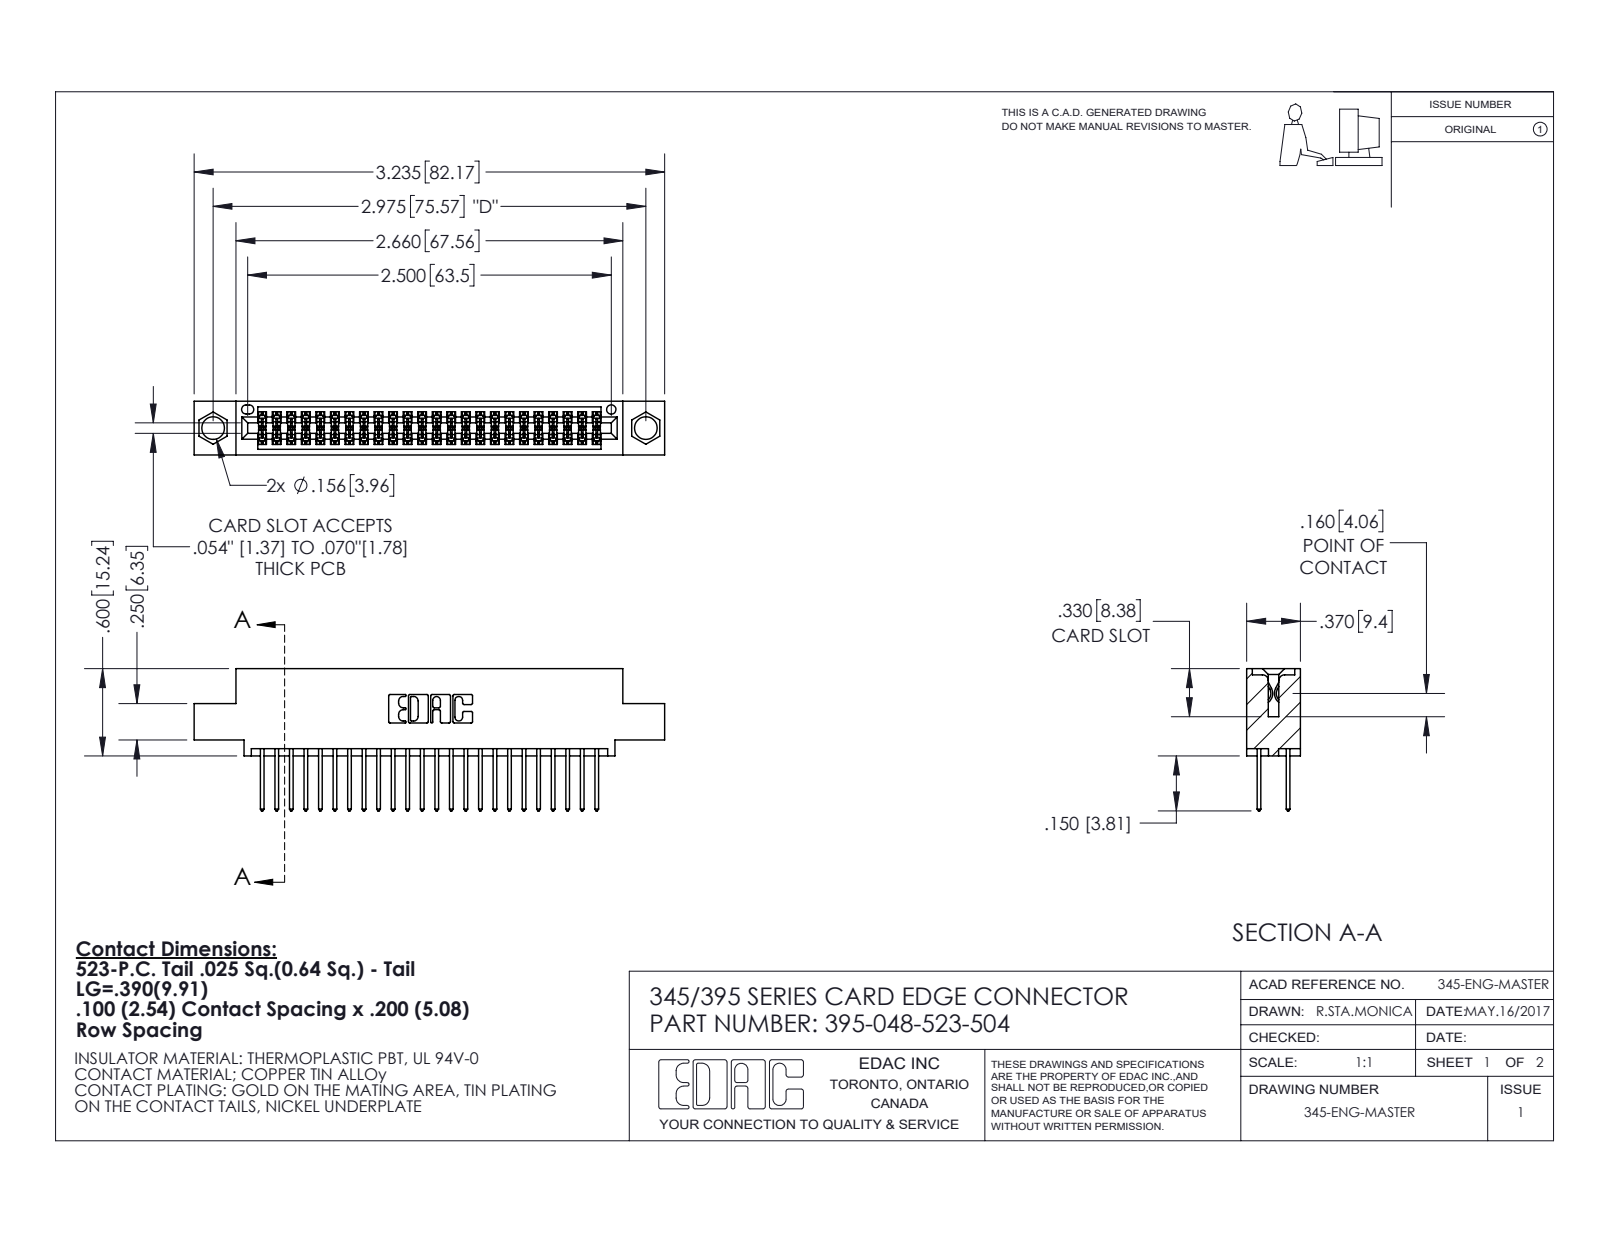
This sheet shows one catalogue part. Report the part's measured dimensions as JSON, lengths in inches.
{"part_name": "345 Part_0.110 Offset - 0.156 Dia-TI; 395-048-523-504; 345-292-001_345-293-123", "step_written_by": "SolidWorks 2020 (CONFIG_CONTROL_DESIGN)", "units": "inches", "bodies": {"solids": 49, "faces": 2544, "planar": 1682, "cylindrical": 862, "other": 0}, "overall_size": [3.235, 0.977, 0.37], "volume_in3": 0.472, "surface_area_in2": 17.78, "round_holes": [[0.156, 2], [0.064, 1]], "partial_cylinders_radius": [[0.006, 72], [0.01, 48], [0.01, 22], [0.007, 6], [0.031, 6], [0.026, 3], [0.014, 2], [0.019, 2]], "face_to_face_distances": [0.298, 0.072, 0.2, 0.098, 0.272, 0.025, 0.37, 0.225, 0.175, 0.149], "hole_center_spacings": [0.27, 2.741, 2.975]}
